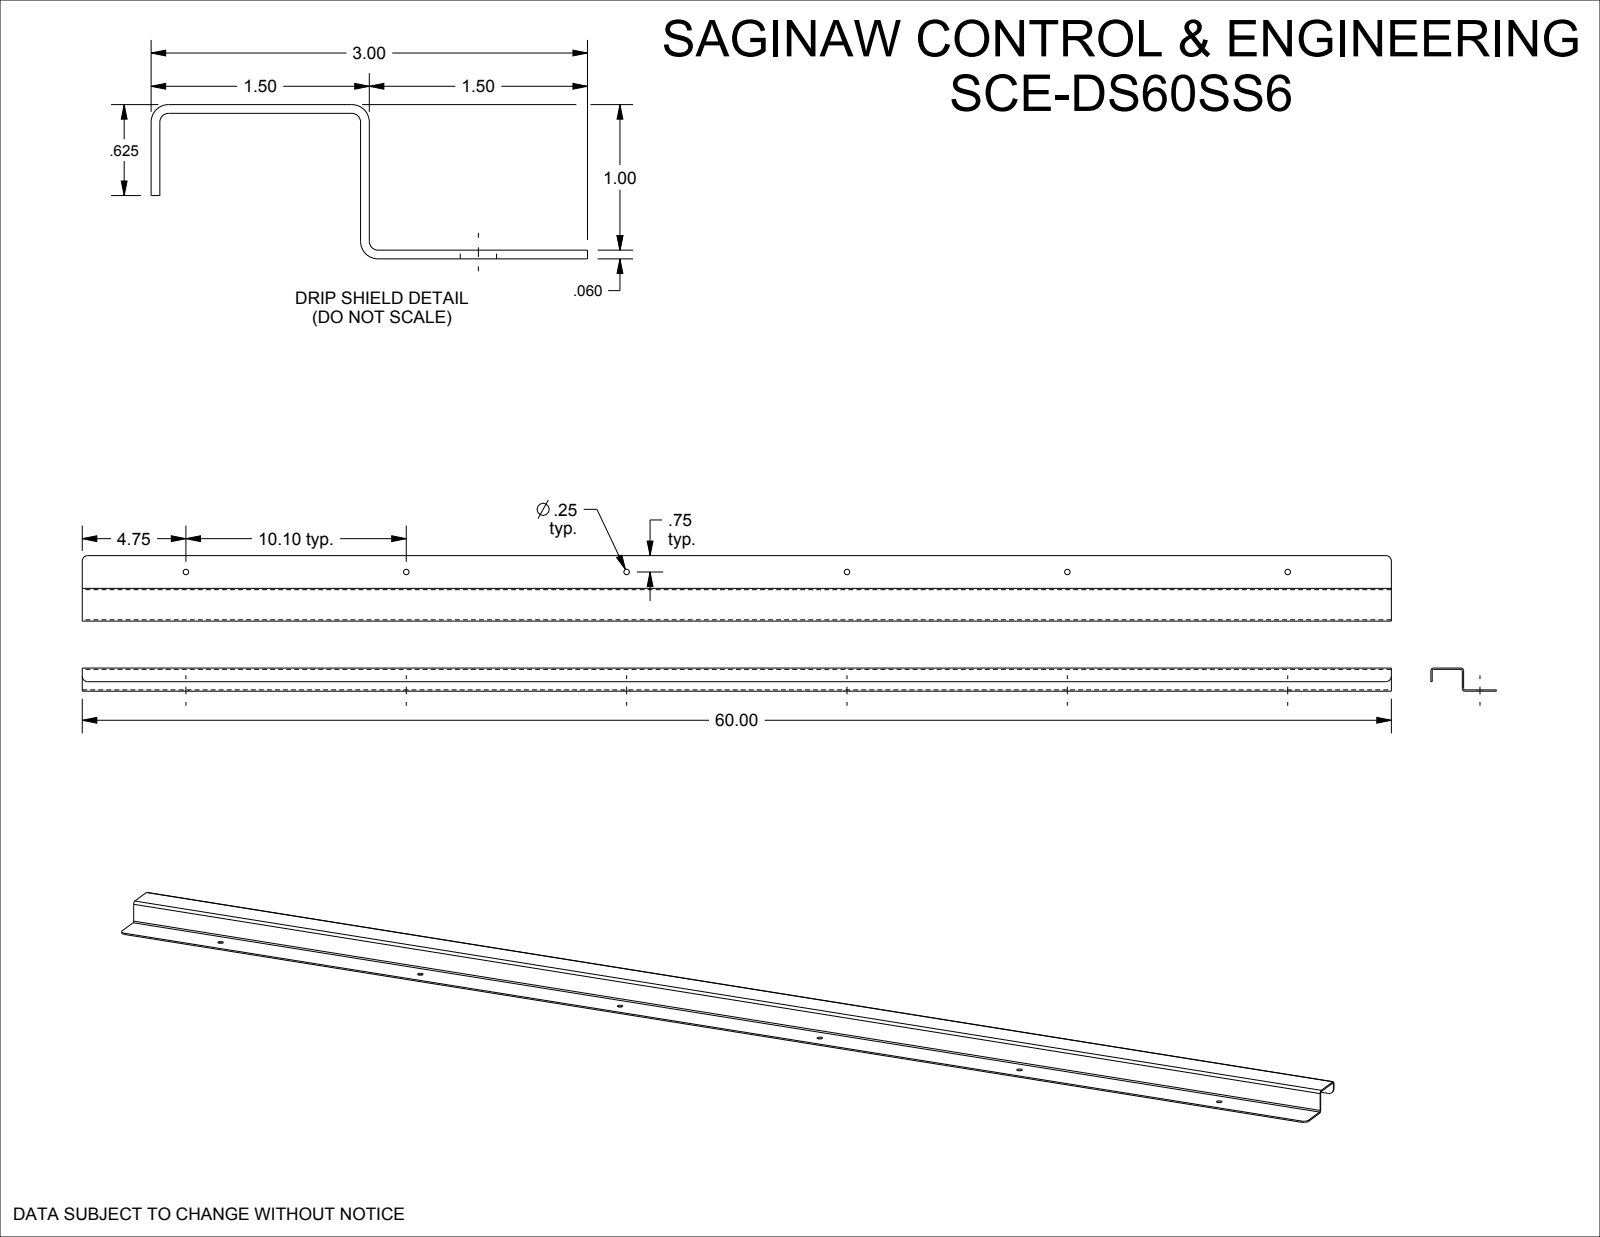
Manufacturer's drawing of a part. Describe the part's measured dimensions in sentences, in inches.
The part is named "SCE-DS60SS6". Its 3-D file was written by "SolidWorks 2019 (CONFIG_CONTROL_DESIGN)". It is 1 solid with 28 faces: 12 planar, 16 cylindrical and 0 other. Overall it measures 60 by 3 by 1.06 inches. Its volume is 16 cubic inches and its surface area 541.2 square inches. Round holes: 6 of diameter 0.25. Partial cylindrical surfaces (rounded edges, fillets, slot ends): 4 of radius 0.25, 3 of radius 0.06, 3 of radius 0.12. The main face-to-face distances are 0.06, 1, 1.06, 0.94, 1.44, 1.5, 1.38, 0.435, 0.375, 0.565. The hole center spacings are 10.1, 20.2, 30.3, 40.4, 50.5.
